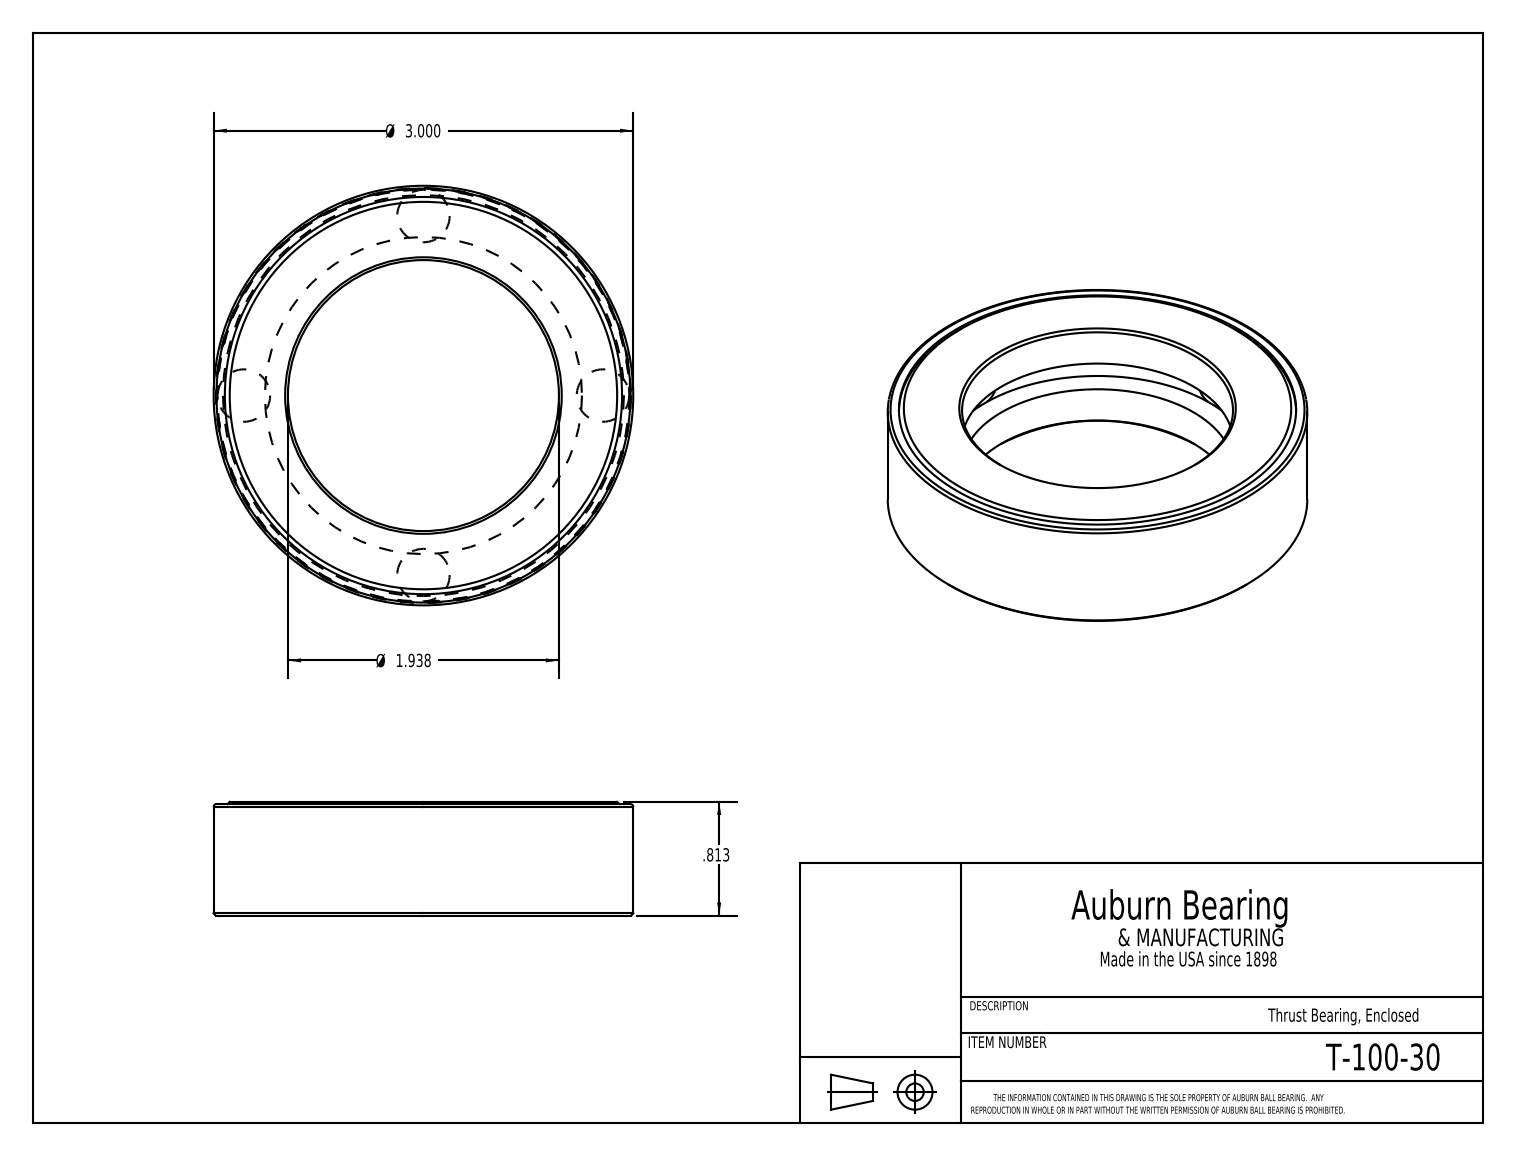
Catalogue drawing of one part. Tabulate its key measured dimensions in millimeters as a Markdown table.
| quantity | value |
| --- | --- |
| part name | T-100-30 |
| STEP written by | SolidWorks 2016 (CONFIG_CONTROL_DESIGN) |
| units | millimeters |
| bodies | 6 solids, 28 faces (9 planar, 7 cylindrical, 12 other) |
| overall size | 76.2 × 76.2 × 20.7 |
| volume | 37 180 mm³ |
| surface area | 24 110 mm² |
| round holes (diameter × count) | 49.2 × 1, 72.1 × 1, 75.2 × 1 |
| round bosses / shafts (diameter × count) | 76.2 × 1, 74.8 × 1 |
| main face-to-face distances | 7.5, 13.2, 20.7, 5.7, 20.3, 12.8, 7.1, 0.4, 19.8, 12.3 |
